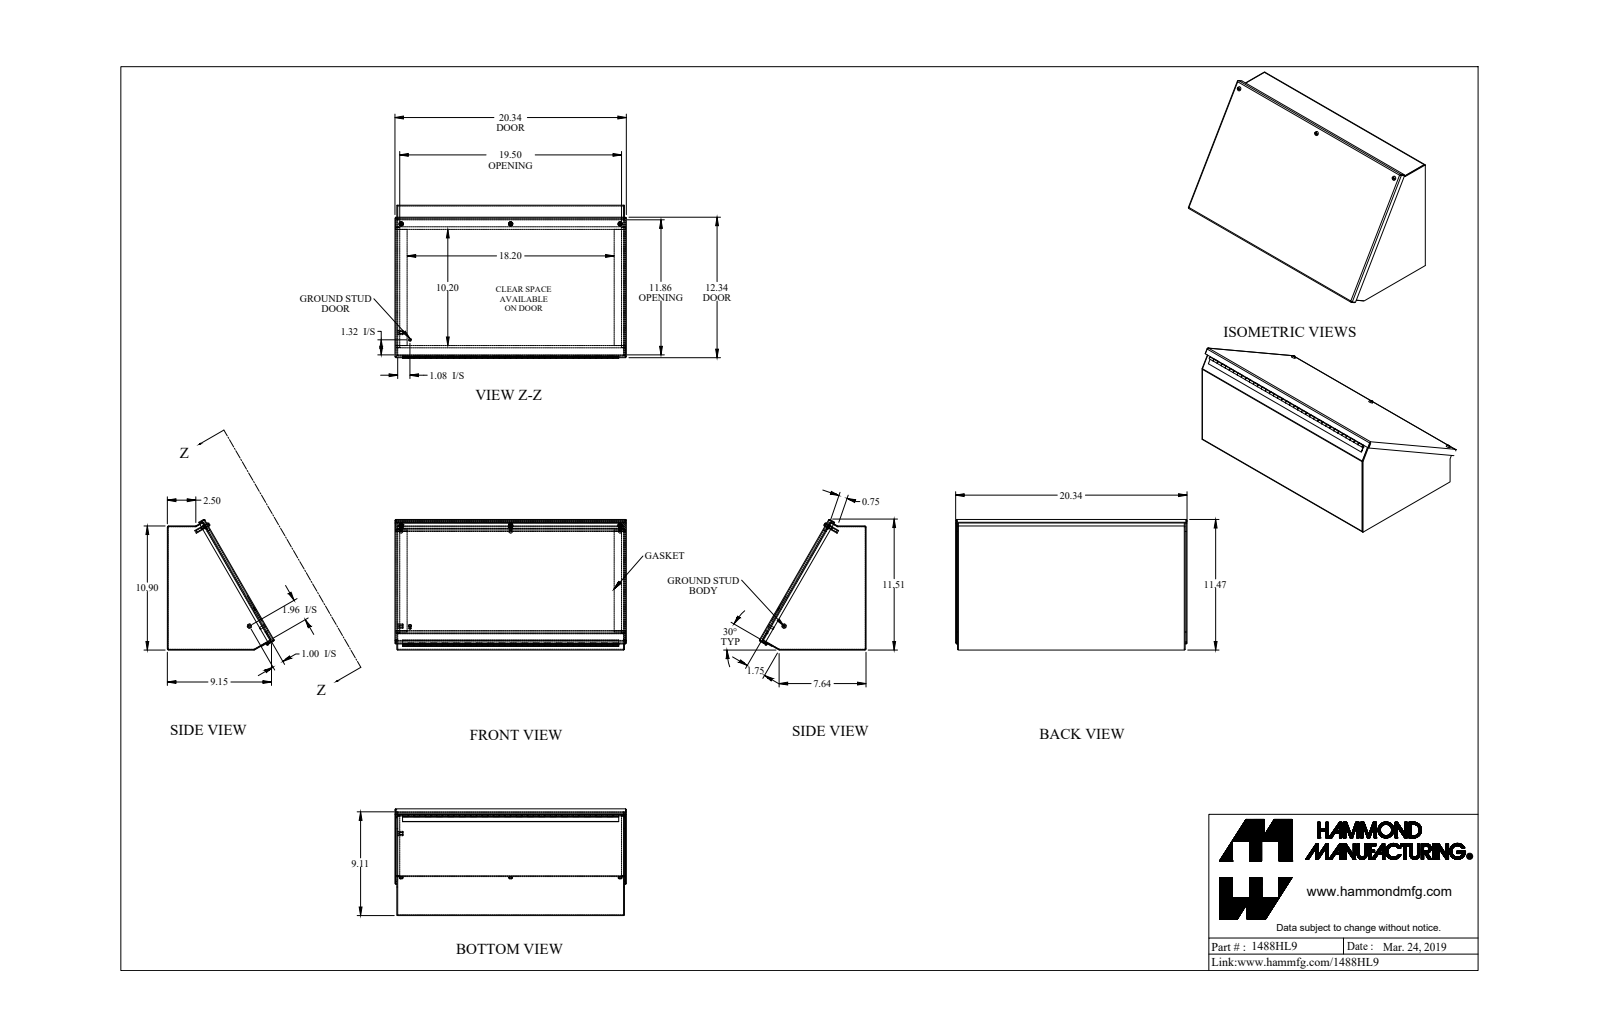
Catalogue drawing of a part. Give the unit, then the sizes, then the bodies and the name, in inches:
Units: inches
Overall size (bounding box): 20.343 × 11.469 × 9.374
Round holes (diameter × count): ⌀0.159 ×3, ⌀0.25 ×3, ⌀0.156 ×1
Round bosses / shafts (diameter × count): ⌀0.39 ×3, ⌀0.275 ×3, ⌀0.19 ×3, ⌀0.148 ×3, ⌀0.375 ×1, ⌀0.25 ×1, ⌀0.188 ×1, ⌀0.174 ×1
Partial cylindrical surfaces — rounded edges, fillets, slot ends (radius × count): R0.036 ×12, R0.108 ×12, R0.125 ×3, R0.16 ×3, R0.171 ×3
Main face-to-face distances: 0.072, 19.928, 10.828, 19.856, 20, 0.072, 0.25, 0.125, 0.197, 10.9
Hole centre spacings: 9.625, 9.625, 19.25, 19.25
Volume: 82.13 in³ · Surface area: 2 053 in²
Bodies: 20 solids, 679 faces (452 planar, 195 cylindrical, 32 other)
Part name (STEP PRODUCT): 1488HL9_Default
STEP written by: SolidWorks 2019 (CONFIG_CONTROL_DESIGN)
